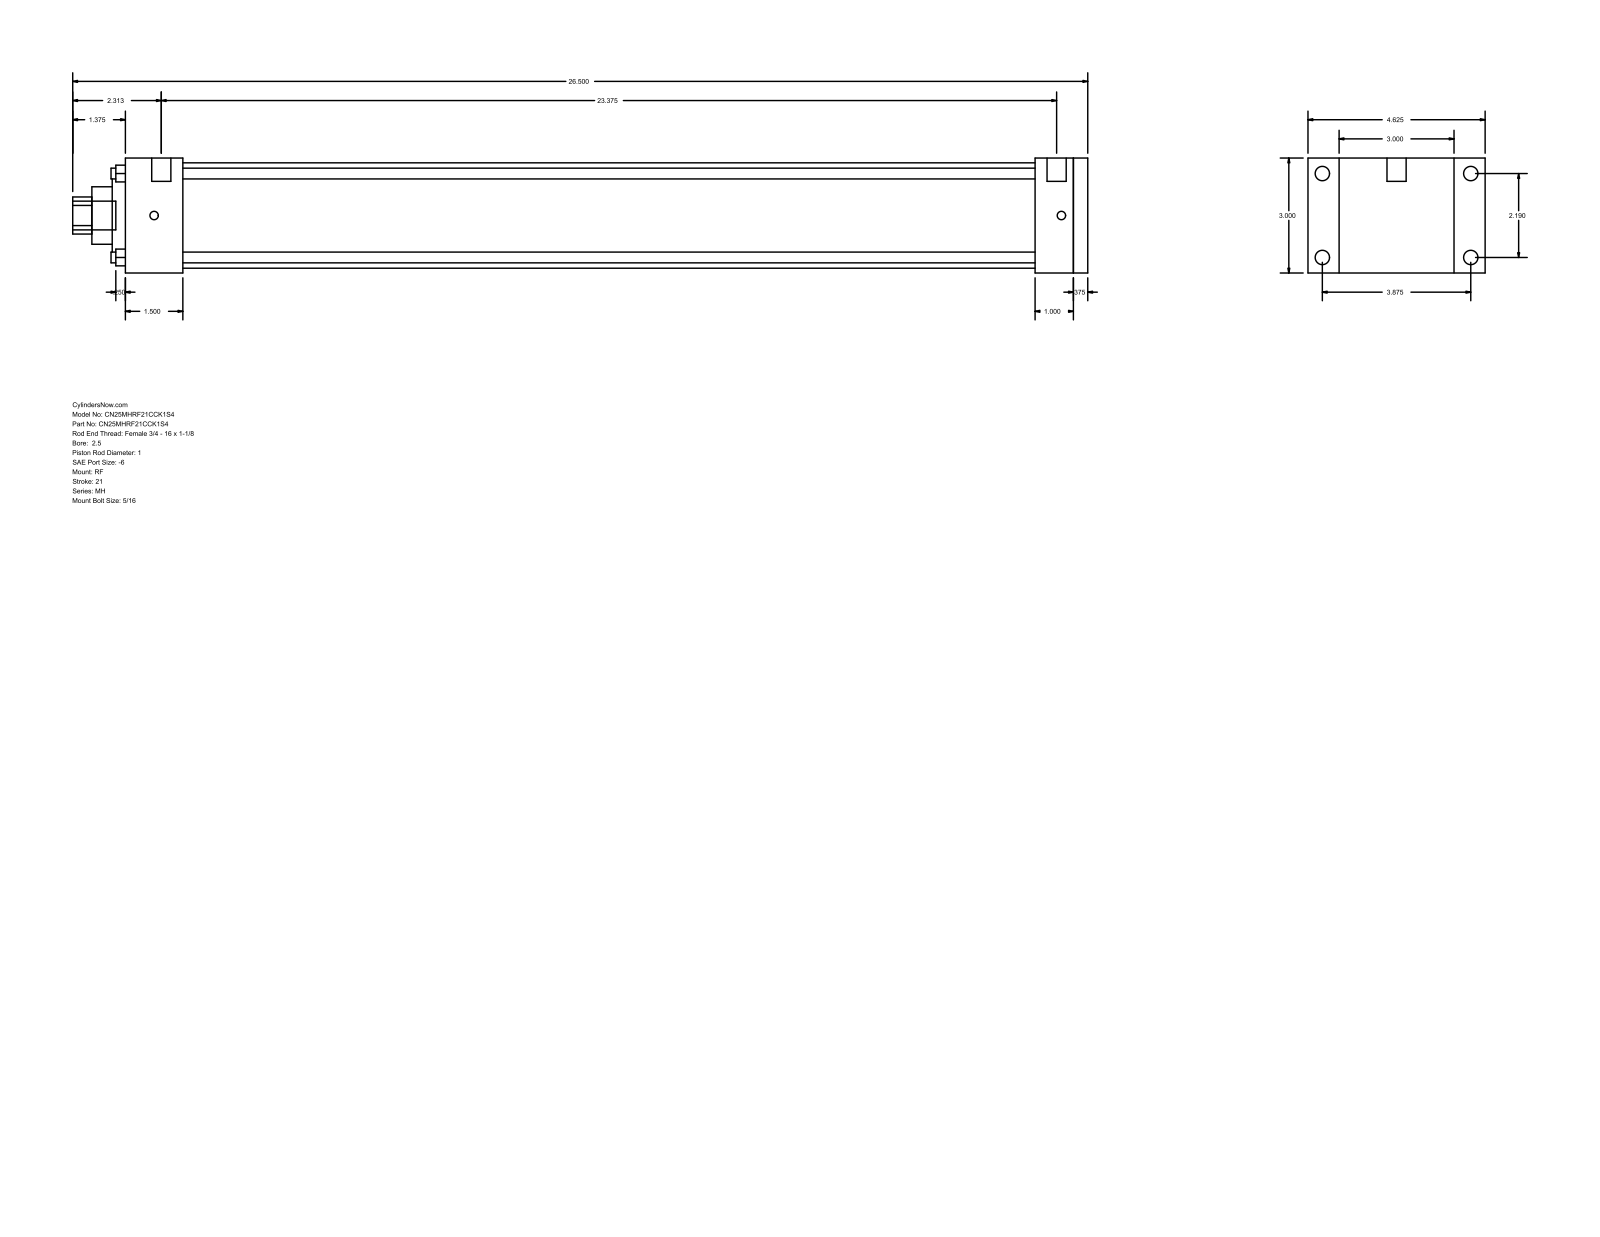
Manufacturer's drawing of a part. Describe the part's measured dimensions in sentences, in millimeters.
The part is named "MH_RF__0250_1". Its 3-D file was written by "GSSL Pune (CONFIG_CONTROL_DESIGN)". It is 0 solids with 94 faces: 65 planar, 29 cylindrical and 0 other. Overall it measures 673.1 by 117.47 by 76.2 millimeters. Round holes: 4 of diameter 7.14, 1 of diameter 25.4, 1 of diameter 38.1, 1 of diameter 60.33, 1 of diameter 69.85. Round bosses or shafts: 4 of diameter 9.53, 4 of diameter 5.56, 2 of diameter 12.7, 1 of diameter 19.05. Partial cylindrical surfaces (rounded edges, fillets, slot ends): 1 of radius 12.29. The main face-to-face distances are 76.2, 9.52, 638.18, 628.66, 603.25, 25.41, 34.93, 38.11, 565.14, 590.55. The hole center spacings are 39.33, 55.62, 78.66.
